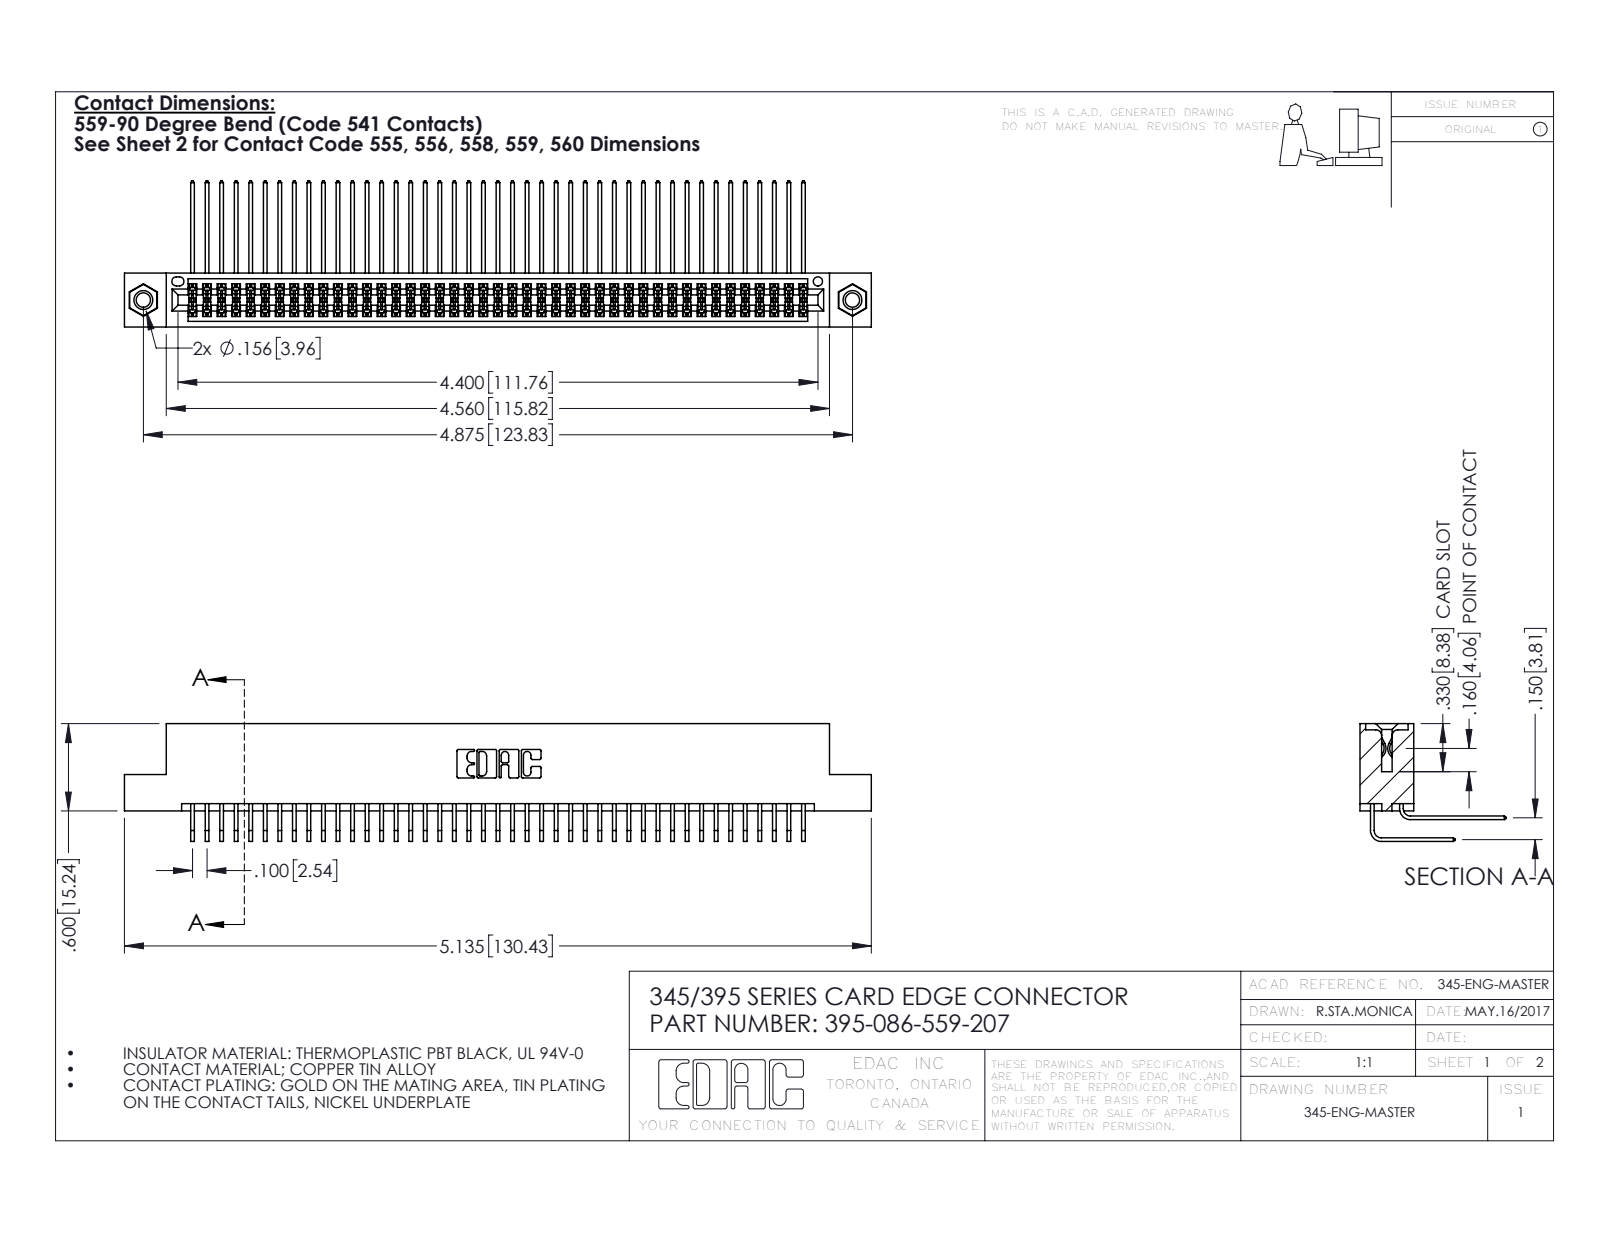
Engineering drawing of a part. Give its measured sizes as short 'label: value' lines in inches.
name: 345-250-001_345-250-005-103; 345 Part_Flush Mounting Lugs - 0.156 Dia-TI; 345-292-001_558 559 Tail - 1; 395-086-559-207 (+1 more)
written by: SolidWorks 2016 (CONFIG_CONTROL_DESIGN)
unit: in
bodies: 89 solids, 4658 faces (3122 planar, 1520 cylindrical, 16 other)
size: 5.135 × 1.005 × 0.809
volume: 0.803 in³; area: 33.85 in²
holes: 2× ⌀0.098, 2× ⌀0.125, 2× ⌀0.156, 1× ⌀0.064
bosses: 2× ⌀0.155
rounds: 130× R0.006, 22× R0.01, 6× R0.007, 6× R0.031, 3× R0.026, 2× R0.014, 2× R0.019, 2× R0.022
face distances: 0.072, 0.298, 0.2, 0.37, 0.098, 0.272, 0.025, 0.225, 0.175, 0.15
hole spacings: 0.27, 4.639, 4.875
